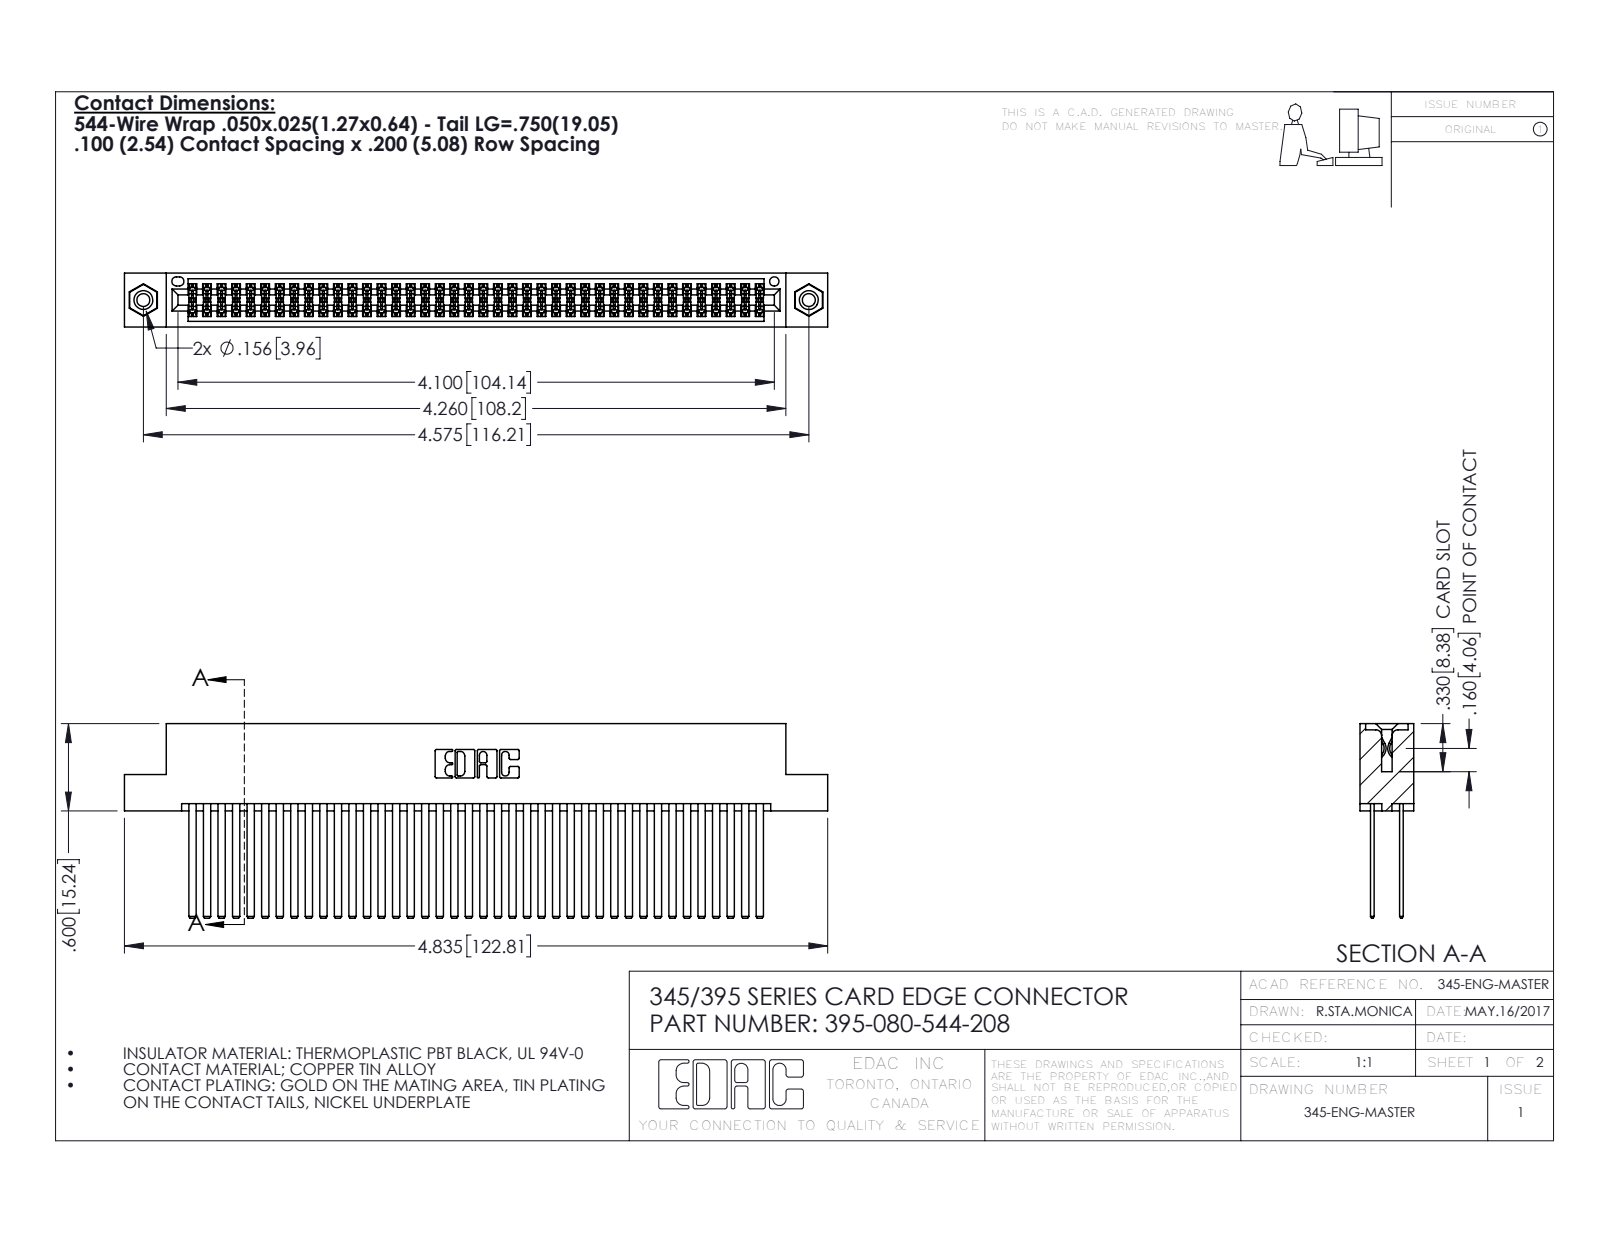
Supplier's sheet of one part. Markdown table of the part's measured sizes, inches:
| quantity | value |
| --- | --- |
| part name | 345-292-001_345-293-144; 345-250-001_345-250-003-102; 345 Part_Flush Mounting Lugs - 0.156 Dia-TI; 395-080-544-208 |
| STEP written by | SolidWorks 2016 (CONFIG_CONTROL_DESIGN) |
| units | inches |
| bodies | 83 solids, 3706 faces (2432 planar, 1258 cylindrical, 16 other) |
| overall size | 4.835 × 1.337 × 0.37 |
| volume | 0.795 in³ |
| surface area | 34.9 in² |
| round holes (diameter × count) | 0.089 × 2, 0.125 × 2, 0.156 × 2, 0.064 × 1 |
| round bosses / shafts (diameter × count) | 0.155 × 2 |
| partial cylindrical surfaces (radius × count) | 0.006 × 120, 0.01 × 22, 0.007 × 6, 0.031 × 6, 0.026 × 3, 0.014 × 2, 0.019 × 2, 0.022 × 2 |
| main face-to-face distances | 0.2, 0.025, 0.072, 0.098, 0.272, 0.298, 0.225, 0.175, 0.37, 0.05 |
| hole center spacings | 0.27, 4.339, 4.575 |
